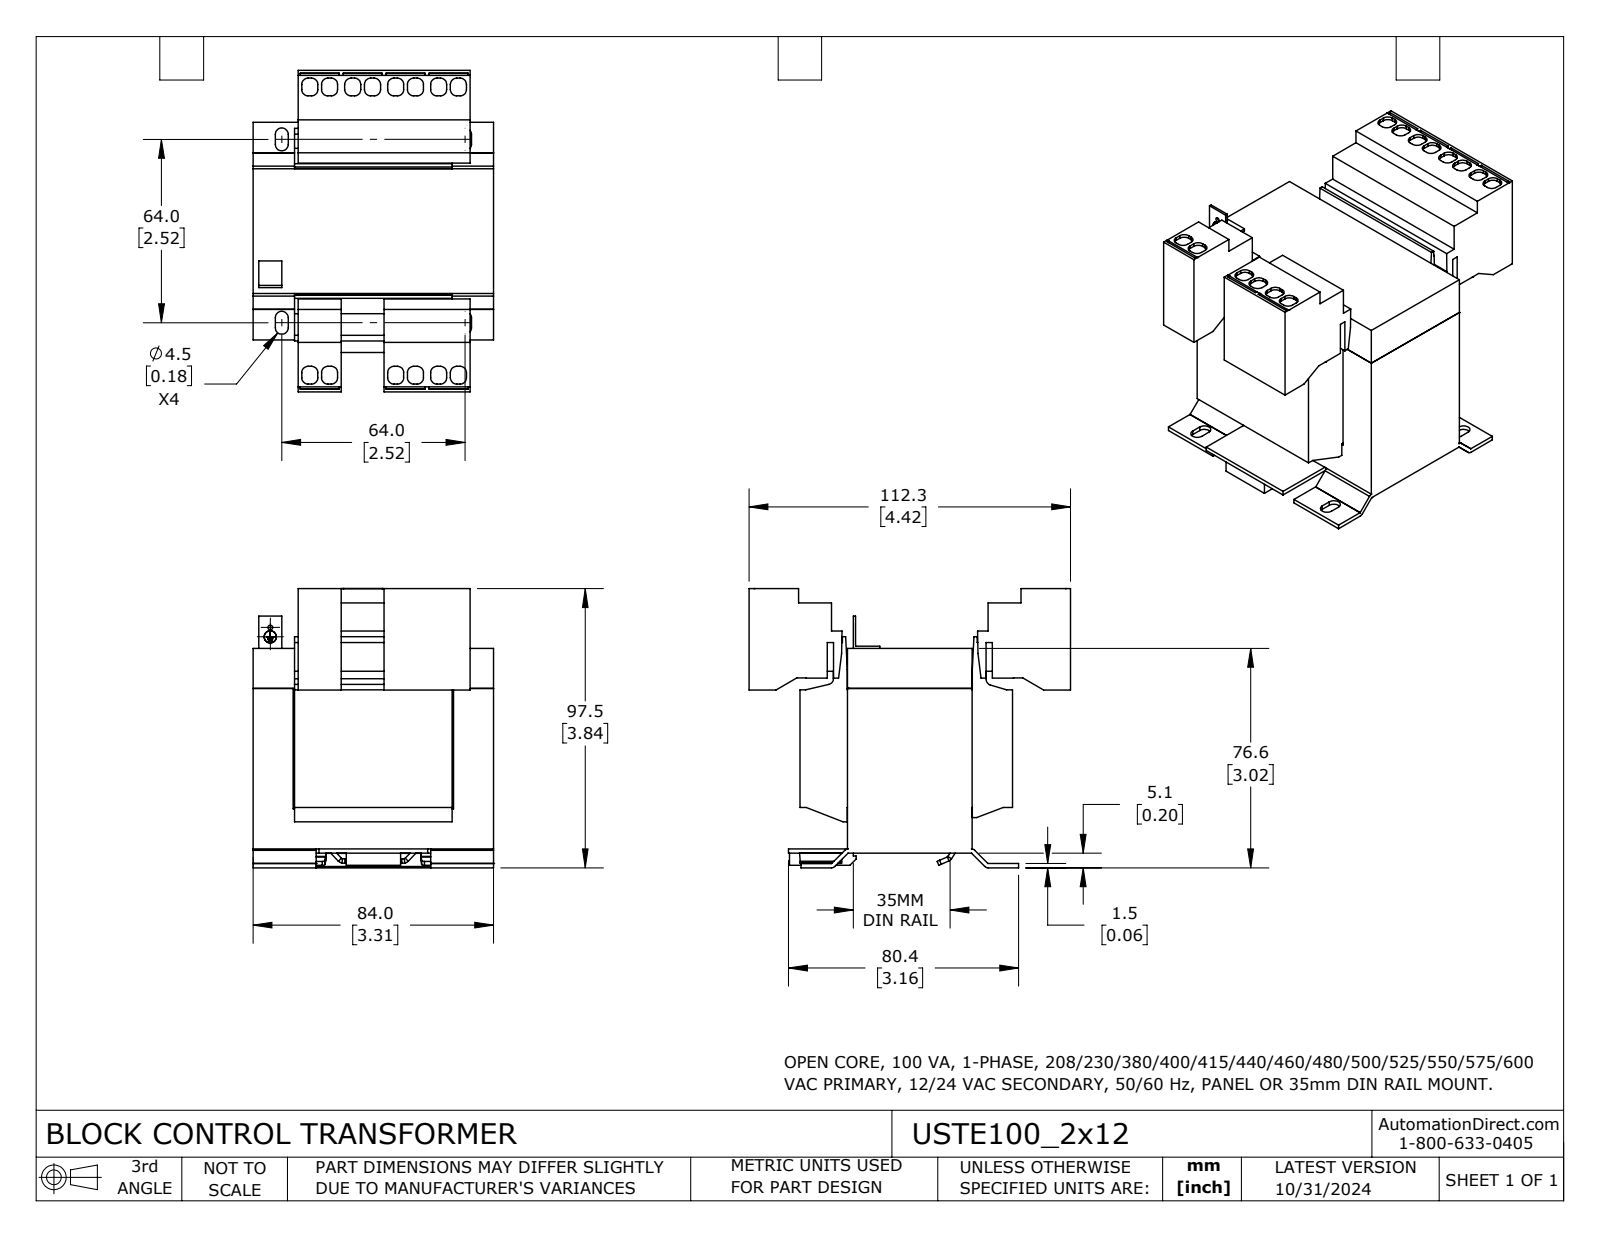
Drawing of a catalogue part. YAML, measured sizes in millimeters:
part_name: "USTE100_2x12"
step_written_by: "SolidWorks 2023 (CONFIG_CONTROL_DESIGN)"
units: millimeters
bodies: {solids: 1, faces: 555, planar: 437, cylindrical: 106, other: 12}
overall_size: [112.3, 97.5, 84]
volume: 426400
surface_area: 86450
round_holes:
  - {diameter: 1.7, count: 1}
  - {diameter: 4.3, count: 1}
round_bosses_or_shafts:
  - {diameter: 4.2, count: 1}
partial_cylinders:
  - {radius: 2.2, count: 56}
  - {radius: 2, count: 9}
  - {radius: 2.3, count: 8}
  - {radius: 0.1, count: 4}
  - {radius: 1, count: 4}
  - {radius: 1.6, count: 4}
  - {radius: 0.5, count: 3}
face_to_face_distances: [14, 14.5, 69.5, 70, 1, 76.9, 0.5, 56, 84, 34.4]
hole_center_spacings: [3.3]
